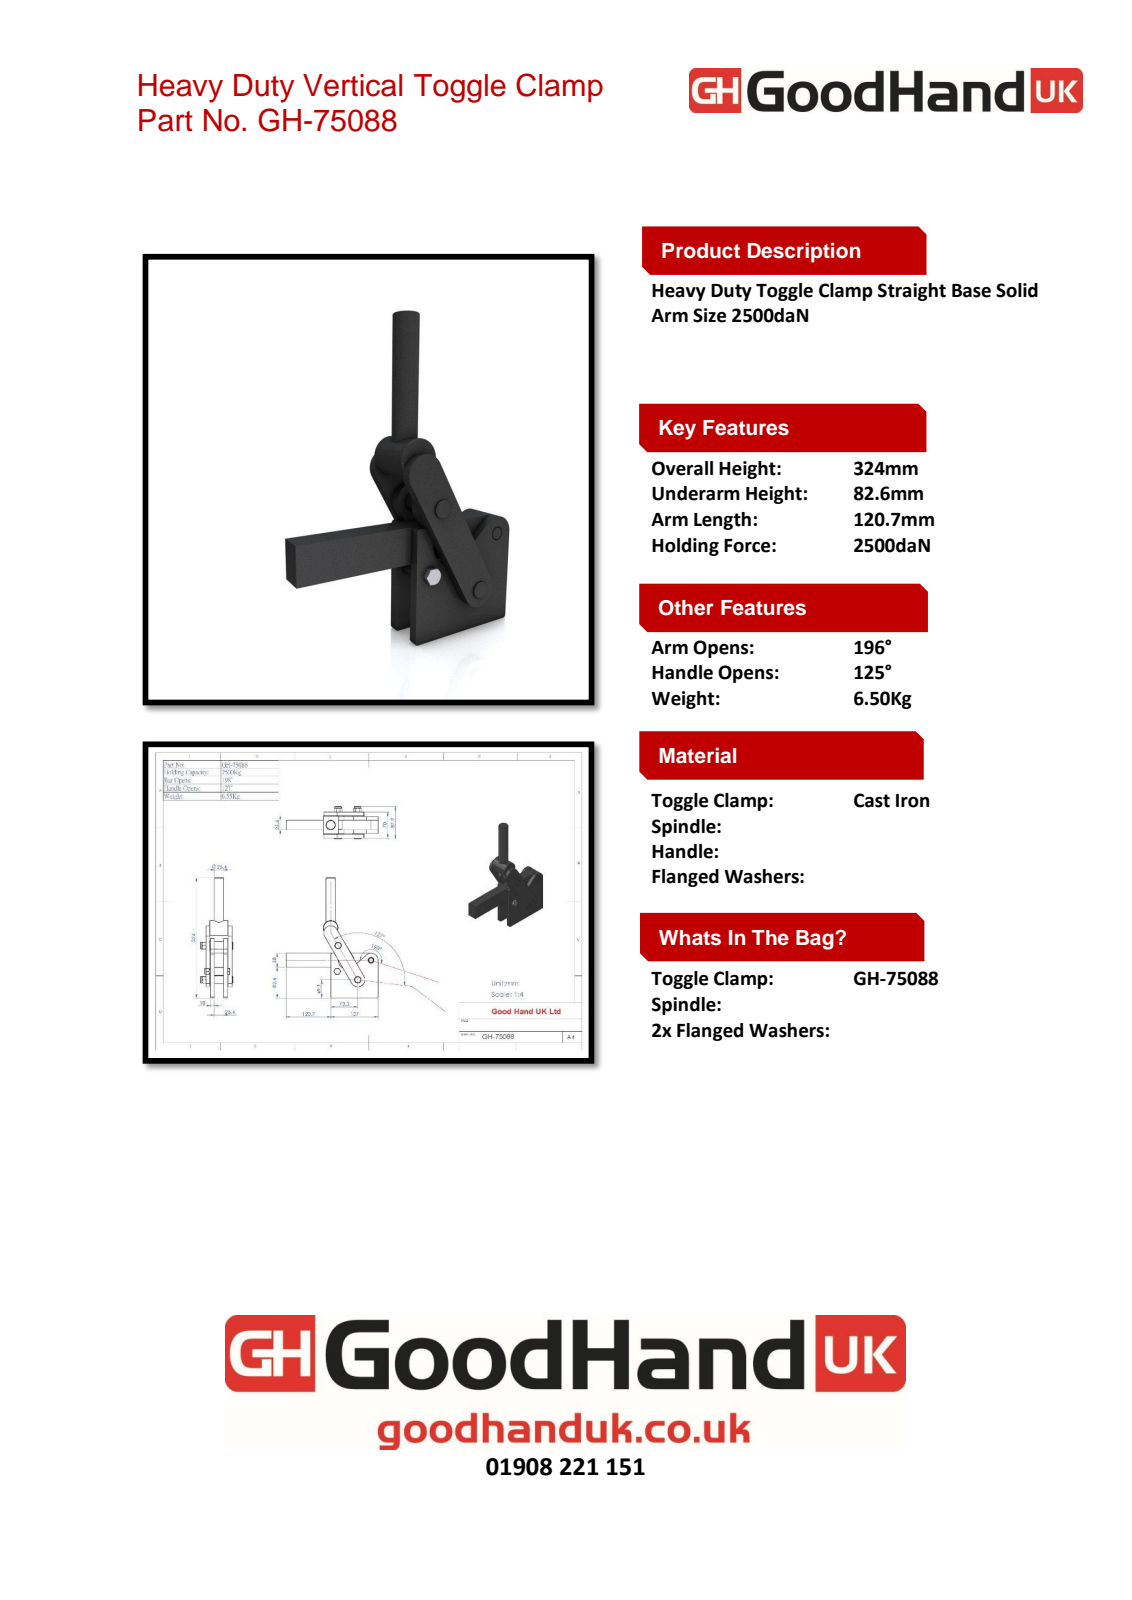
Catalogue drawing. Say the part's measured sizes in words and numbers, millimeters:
The part is named "Group1^GH-75088(簡化); GH-75088(簡化); Group4^GH-75088(簡化); 4708808-2^GH-75088(簡化) (+1 more)". Its 3-D file was written by "SolidWorks 2016 (AUTOMOTIVE_DESIGN)". It is 4 solids with 212 faces: 85 planar, 75 cylindrical and 52 other. Overall it measures 324 by 247.65 by 83.37 millimeters. Its volume is 835 236 cubic millimeters and its surface area 176 779 square millimeters. Round holes: 4 of diameter 11. Round bosses or shafts: 2 of diameter 28, 2 of diameter 18, 2 of diameter 16, 2 of diameter 13.9, 1 of diameter 40, 1 of diameter 25.4, 1 of diameter 11. Partial cylindrical surfaces (rounded edges, fillets, slot ends): 5 of radius 19, 3 of radius 3, 1 of radius 23.75. The main face-to-face distances are 10, 35.4, 12.3, 47.7, 25.4, 45.4, 2.3, 37.7, 22.3, 57.7. The hole center spacings are 46.34, 60.15, 63.26, 64.66, 97.16, 106.48.
